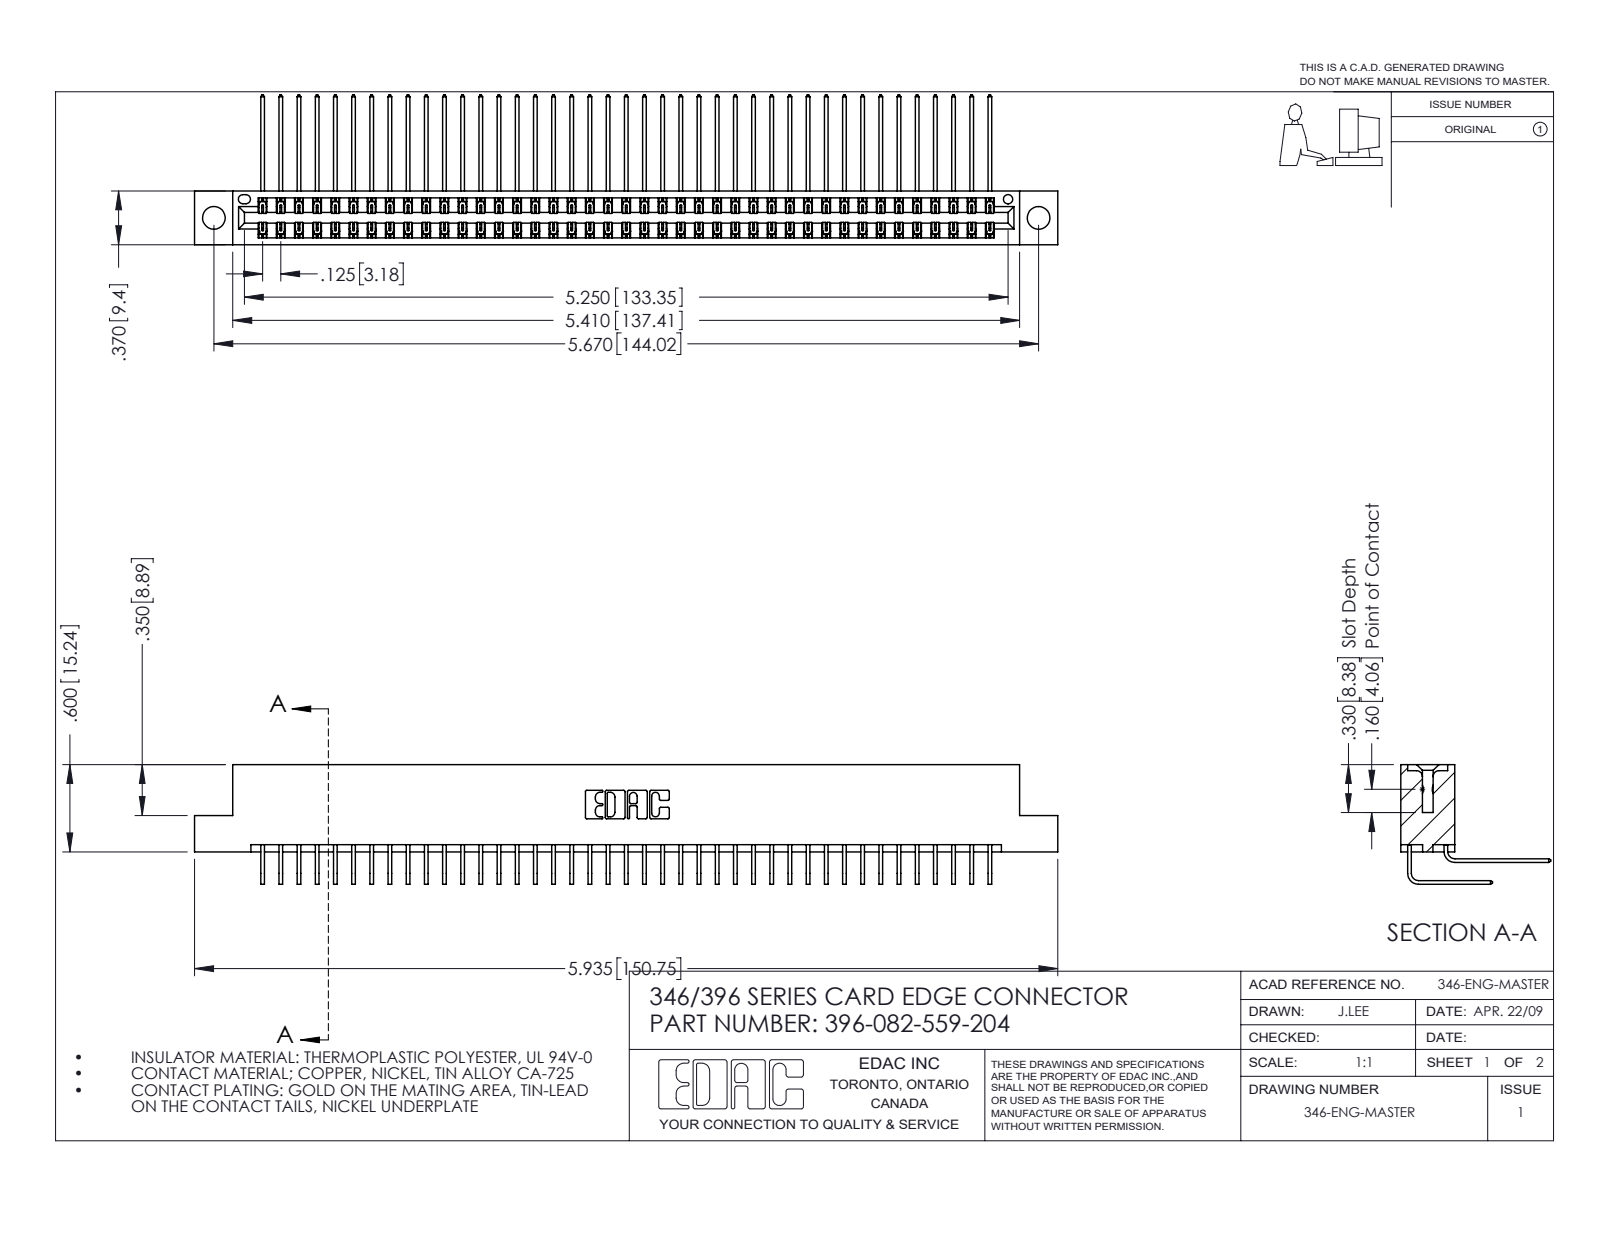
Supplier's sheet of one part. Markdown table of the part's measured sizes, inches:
| quantity | value |
| --- | --- |
| part name | 346 Part_Flush Mounting Lugs - 0.156 Dia-TH; 345-292-001_558 559 Tail - 1; 396-082-559-204; 345-292-001_559 Tail - 2 |
| STEP written by | SolidWorks 2016 (CONFIG_CONTROL_DESIGN) |
| units | inches |
| bodies | 83 solids, 4550 faces (3110 planar, 1440 cylindrical, 0 other) |
| overall size | 5.935 × 1.03 × 0.823 |
| volume | 0.92 in³ |
| surface area | 35.33 in² |
| round holes (diameter × count) | 0.156 × 2, 0.064 × 1 |
| partial cylindrical surfaces (radius × count) | 0.006 × 123, 0.01 × 22, 0.007 × 6, 0.031 × 6, 0.026 × 3, 0.014 × 2, 0.022 × 2, 0.024 × 2 |
| main face-to-face distances | 0.048, 0.322, 0.025, 0.37, 0.25, 0.072, 0.298, 0.275, 0.148, 0.222 |
| hole center spacings | 0.246, 5.461, 5.67 |
